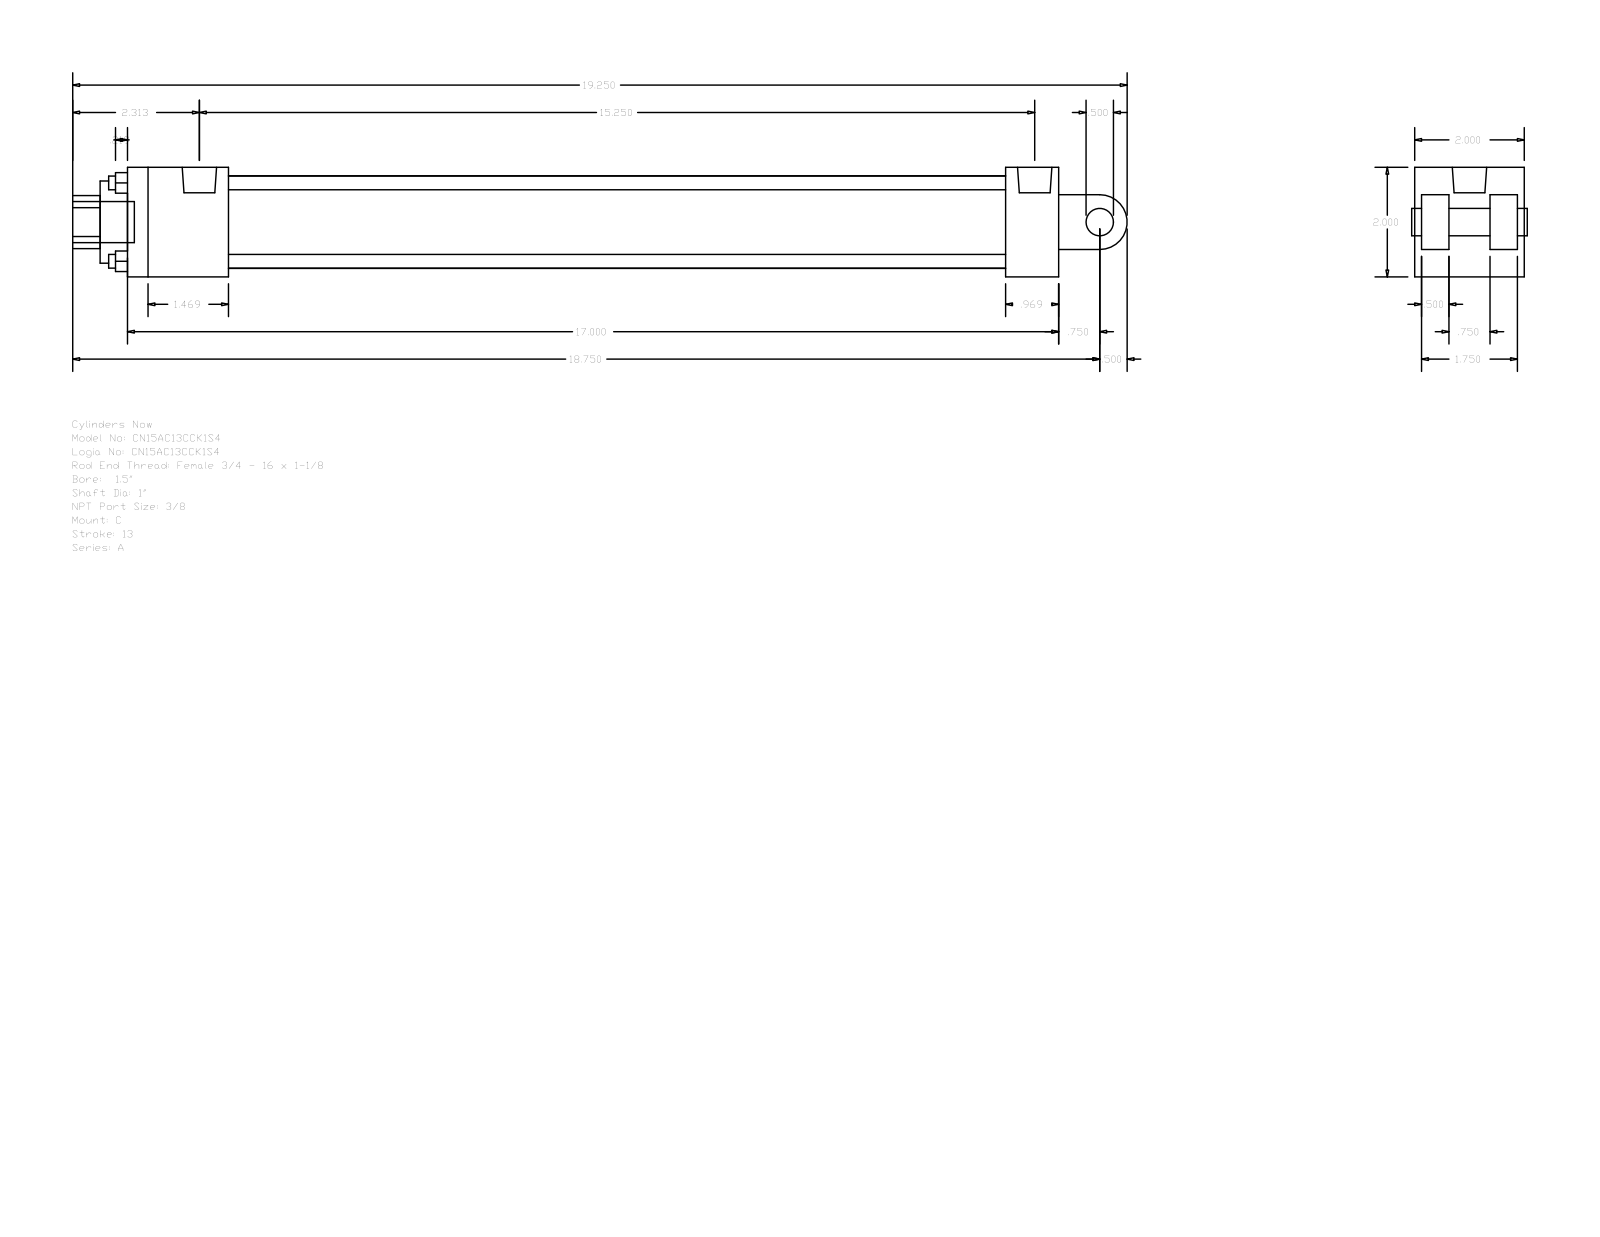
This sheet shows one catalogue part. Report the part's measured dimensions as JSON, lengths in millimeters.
{"part_name": "A_C__0150_1", "step_written_by": "GSSL Pune (CONFIG_CONTROL_DESIGN)", "units": "millimeters", "bodies": {"solids": 0, "faces": 99, "planar": 70, "cylindrical": 29, "other": 0}, "overall_size": [488.95, 50.8, 50.8], "round_holes": [[6.35, 4], [5.56, 2], [15.93, 1], [25.4, 1], [38.1, 1], [42.93, 1]], "round_bosses_or_shafts": [[5.56, 2], [19.05, 1], [15.93, 1], [12.7, 1]], "partial_cylinders_radius": [[12.29, 1], [12.7, 1]], "face_to_face_distances": [50.8, 12.7, 3.17, 15.87, 34.93, 47.63, 31.76, 431.8, 407.19, 24.61], "hole_center_spacings": [25.68, 36.32, 51.36, 3.97]}
